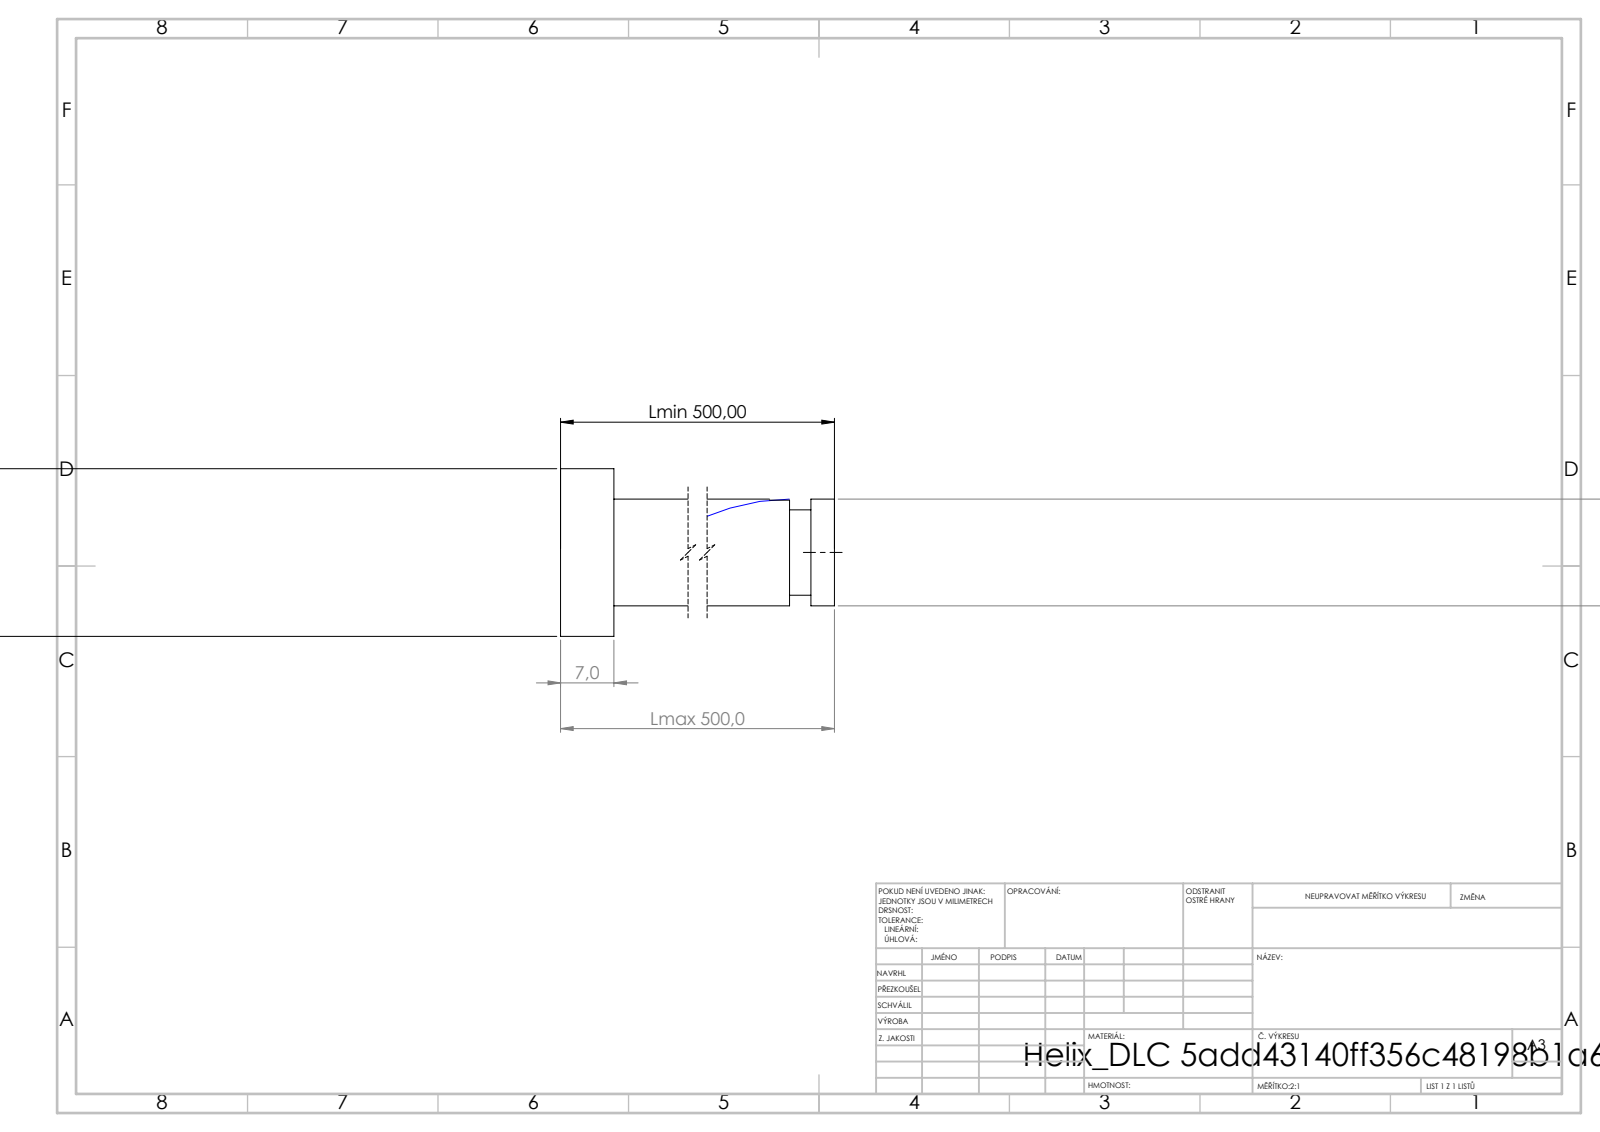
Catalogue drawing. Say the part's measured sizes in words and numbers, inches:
Its 3-D file was written by "SolidWorks 2019 (CONFIG_CONTROL_DESIGN)". It is 1 solid with 21 faces: 6 planar, 14 cylindrical and 1 other. Overall it measures 19.685 by 0.866 by 0.866 inches. Its volume is 4.739 cubic inches and its surface area 36.28 square inches. Round bosses or shafts: 1 of diameter 0.866, 1 of diameter 0.551, 1 of diameter 0.441. The main face-to-face distances are 0.276, 19.685, 19.409, 19.563, 19.288, 0.122, 19.453, 19.178, 0.11, 0.232.
